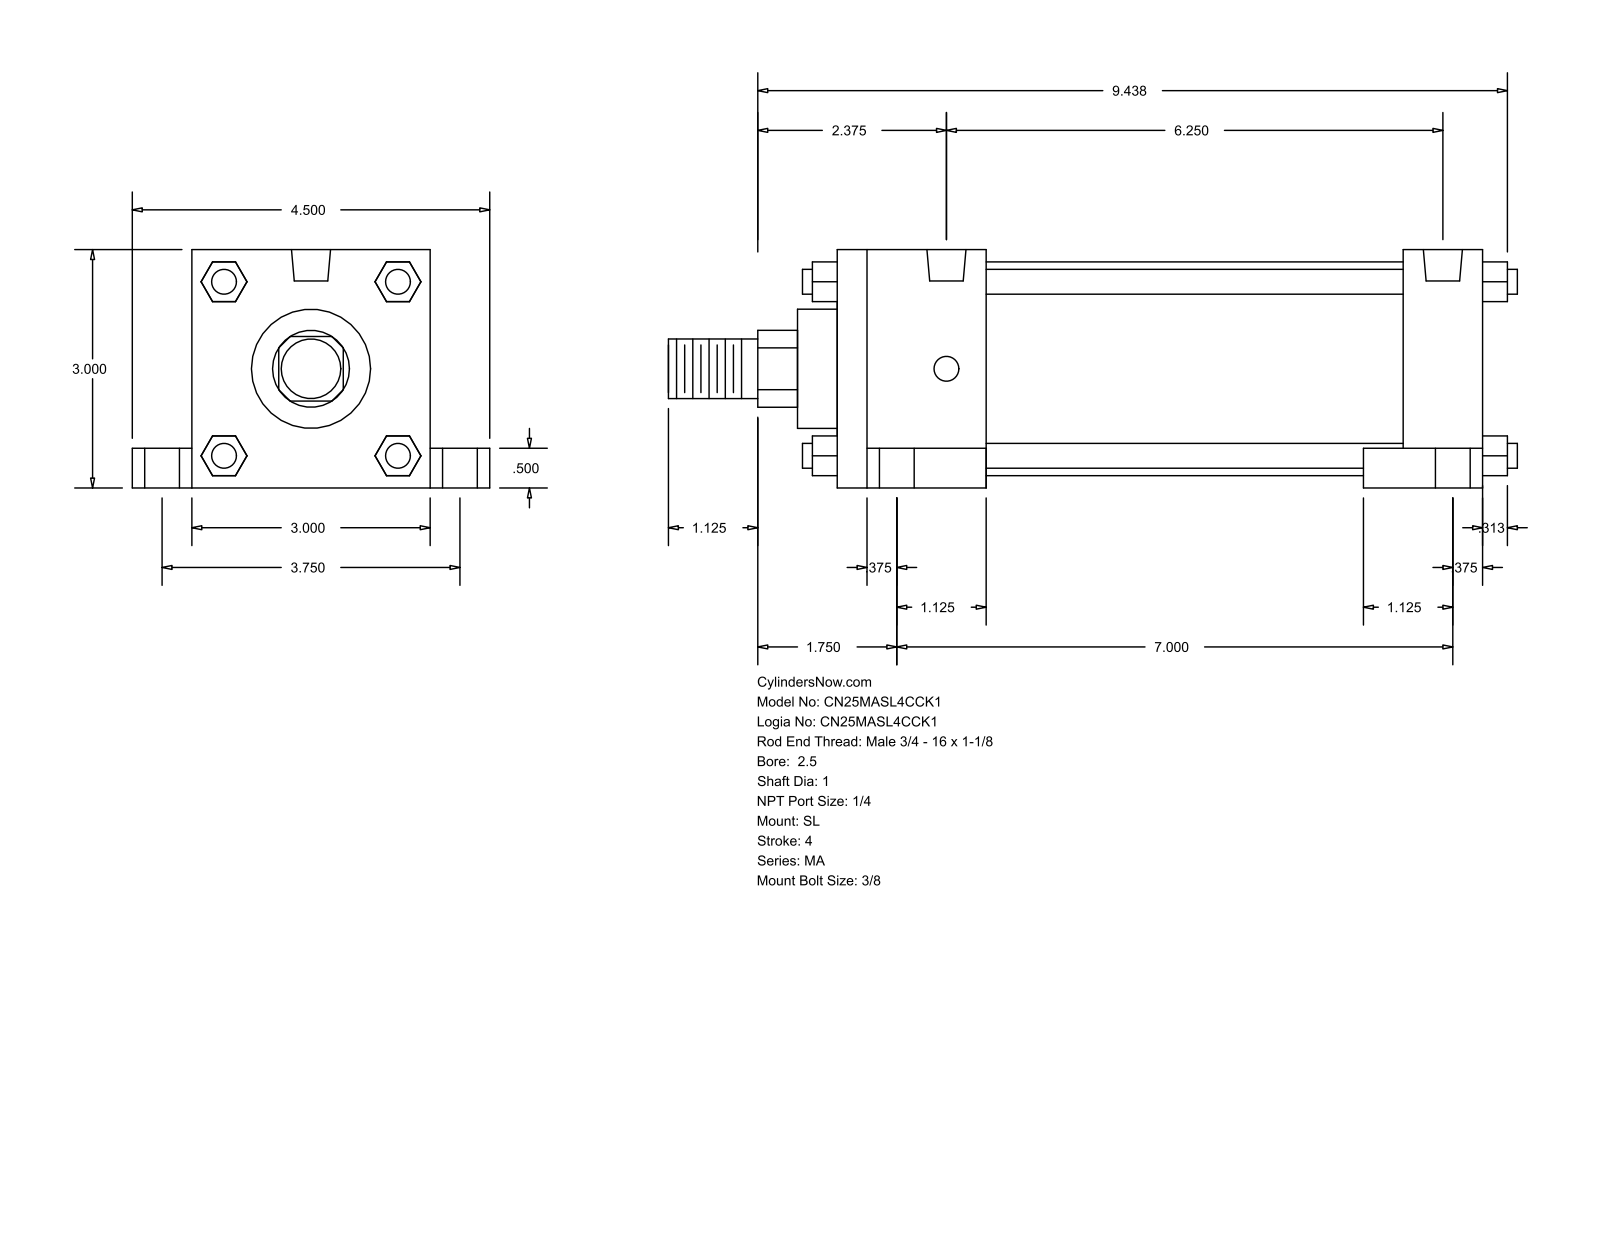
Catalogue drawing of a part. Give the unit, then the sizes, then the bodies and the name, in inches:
Units: inches
Overall size (bounding box): 10.687 × 4.5 × 3
Round holes (diameter × count): ⌀0.313 ×4, ⌀0.437 ×4, ⌀0.687 ×4, ⌀0.492 ×2
Round bosses / shafts (diameter × count): ⌀0.313 ×4, ⌀2.69 ×1, ⌀1.5 ×1, ⌀1 ×1, ⌀0.75 ×1
Partial cylindrical surfaces — rounded edges, fillets, slot ends (radius × count): R0.484 ×1
Main face-to-face distances: 3, 8.125, 0.5, 5.25, 1, 1.875, 6.25, 7.125, 0.75, 3.75
Hole centre spacings: 1.879, 1.976, 3.75, 6.25, 6.645, 7, 7.126, 7.941
Bodies: 0 solids, 148 faces (112 planar, 36 cylindrical, 0 other)
Part name (STEP PRODUCT): MA_SL__0250_1
STEP written by: GSSL Pune (CONFIG_CONTROL_DESIGN)
